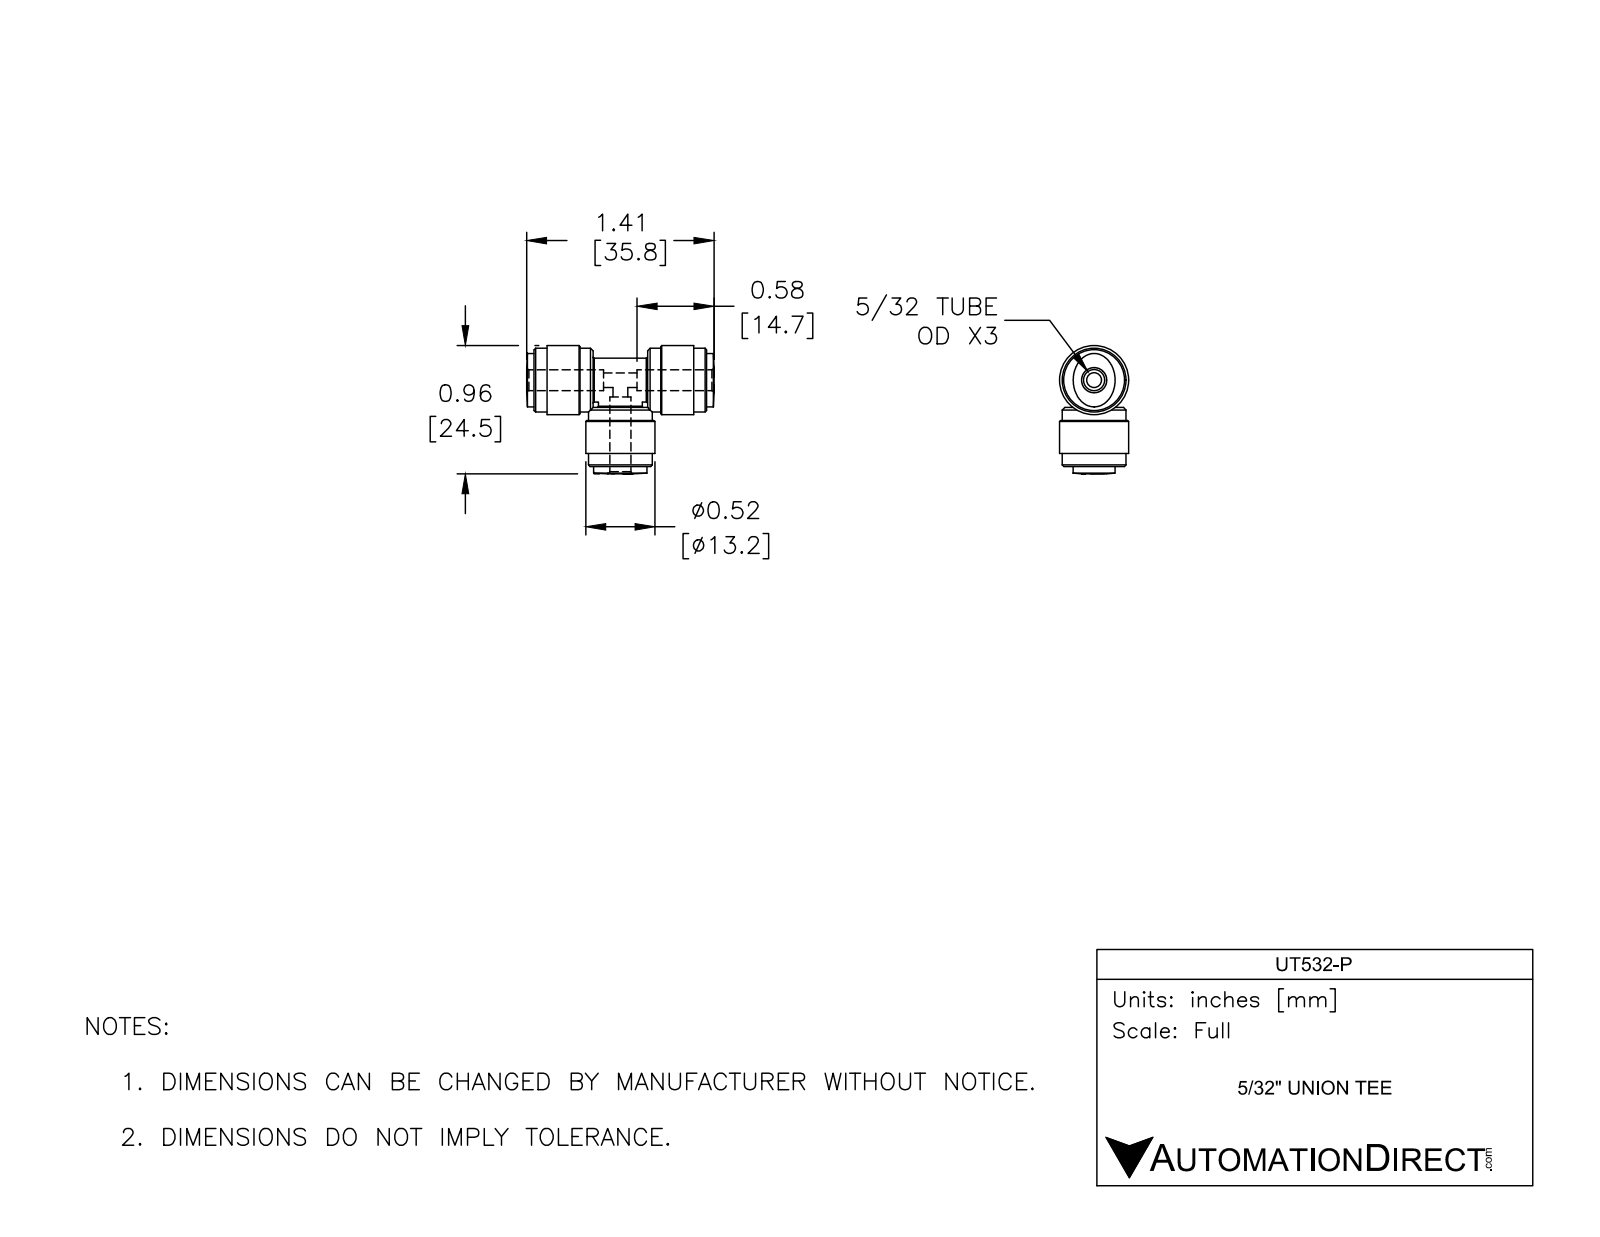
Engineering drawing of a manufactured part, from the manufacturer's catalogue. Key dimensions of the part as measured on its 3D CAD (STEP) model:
Part name (STEP PRODUCT): UT532-P
STEP written by: SolidWorks 2017 (AUTOMOTIVE_DESIGN)
Units: inches
Bodies: 1 solid, 89 faces (15 planar, 32 cylindrical, 42 other)
Overall size (bounding box): 1.409 × 0.965 × 0.52
Volume: 0.283 in³ · Surface area: 4.483 in²
Round holes (diameter × count): ⌀0.11 ×2, ⌀0.157 ×2
Round bosses / shafts (diameter × count): ⌀0.52 ×2, ⌀0.48 ×2, ⌀0.331 ×2
Main face-to-face distances: 0.445, 0.854, 0.098, 0.346, 1.299, 1.201, 0.756, 0.409, 0.248, 0.953
